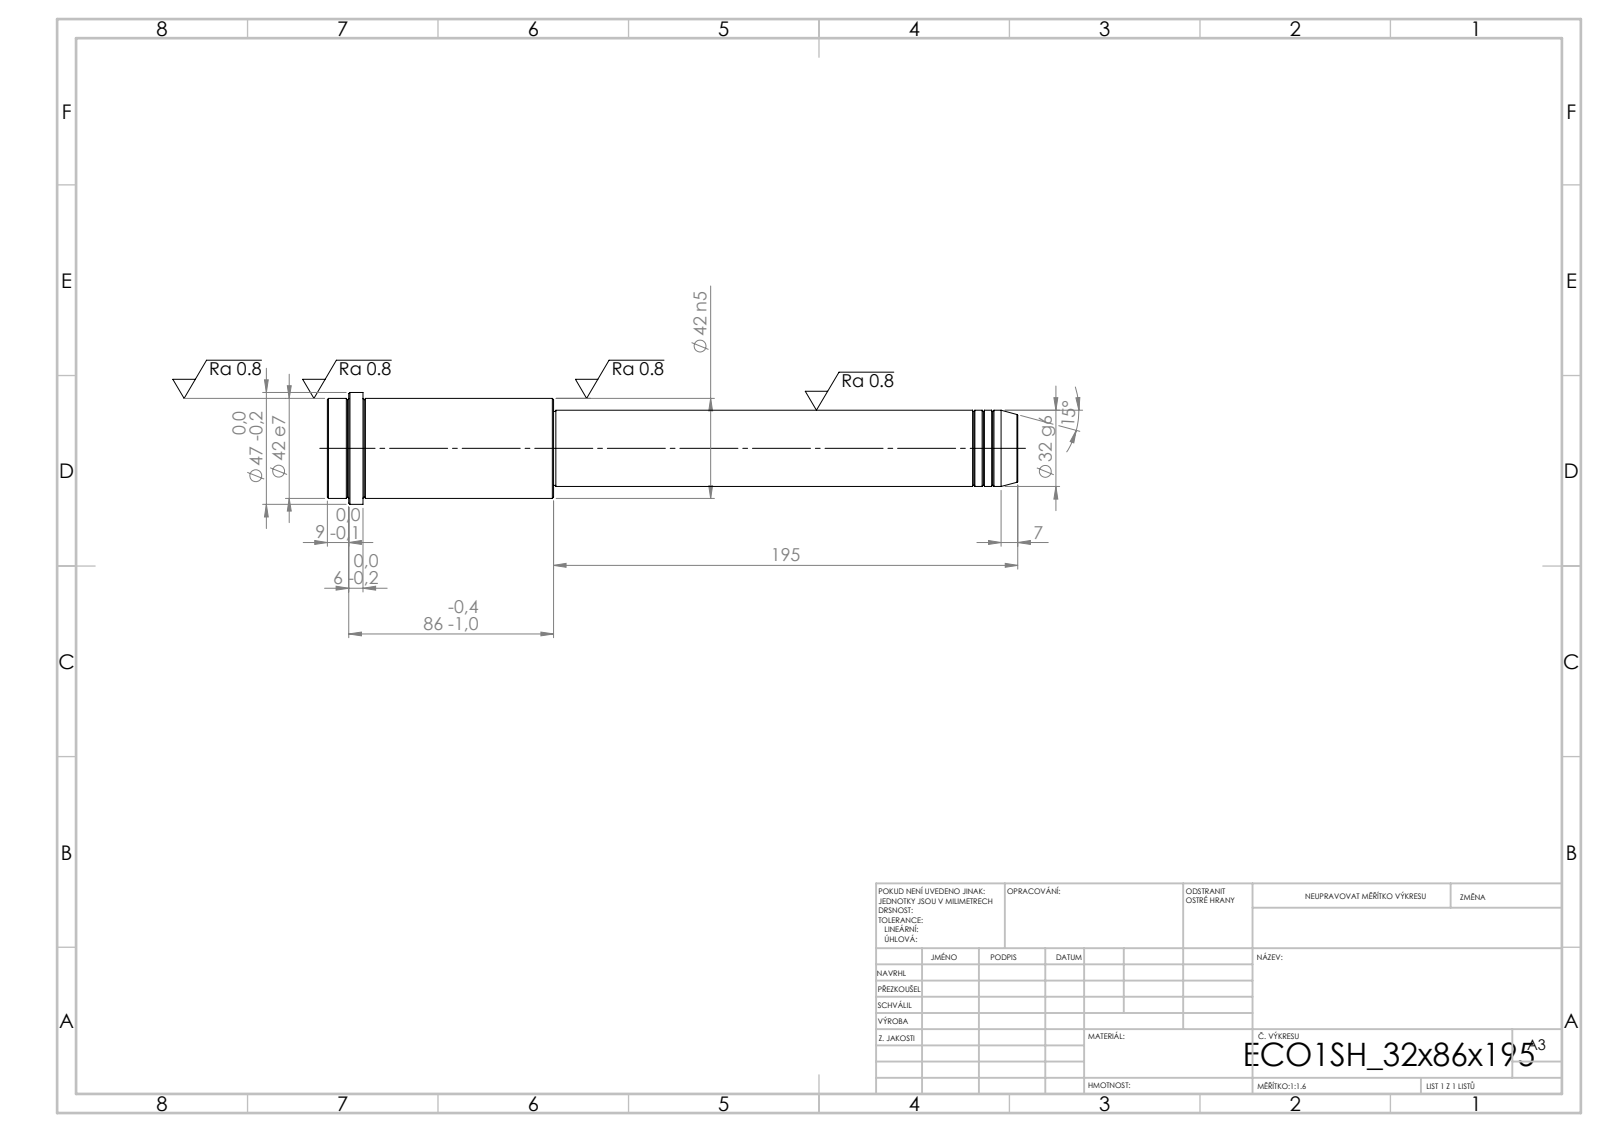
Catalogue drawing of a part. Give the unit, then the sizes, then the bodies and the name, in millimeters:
Units: millimetres
Overall size (bounding box): 290 × 47 × 47
Round bosses / shafts (diameter × count): ⌀47 ×1, ⌀42 ×1, ⌀32 ×1, ⌀31 ×1
Main face-to-face distances: 290, 195, 95, 275, 80, 15, 281, 86, 6, 9
Volume: 289 586 mm³ · Surface area: 35 779 mm²
Bodies: 1 solid, 52 faces (6 planar, 16 cylindrical, 30 other)
STEP written by: SolidWorks 2019 (CONFIG_CONTROL_DESIGN)
